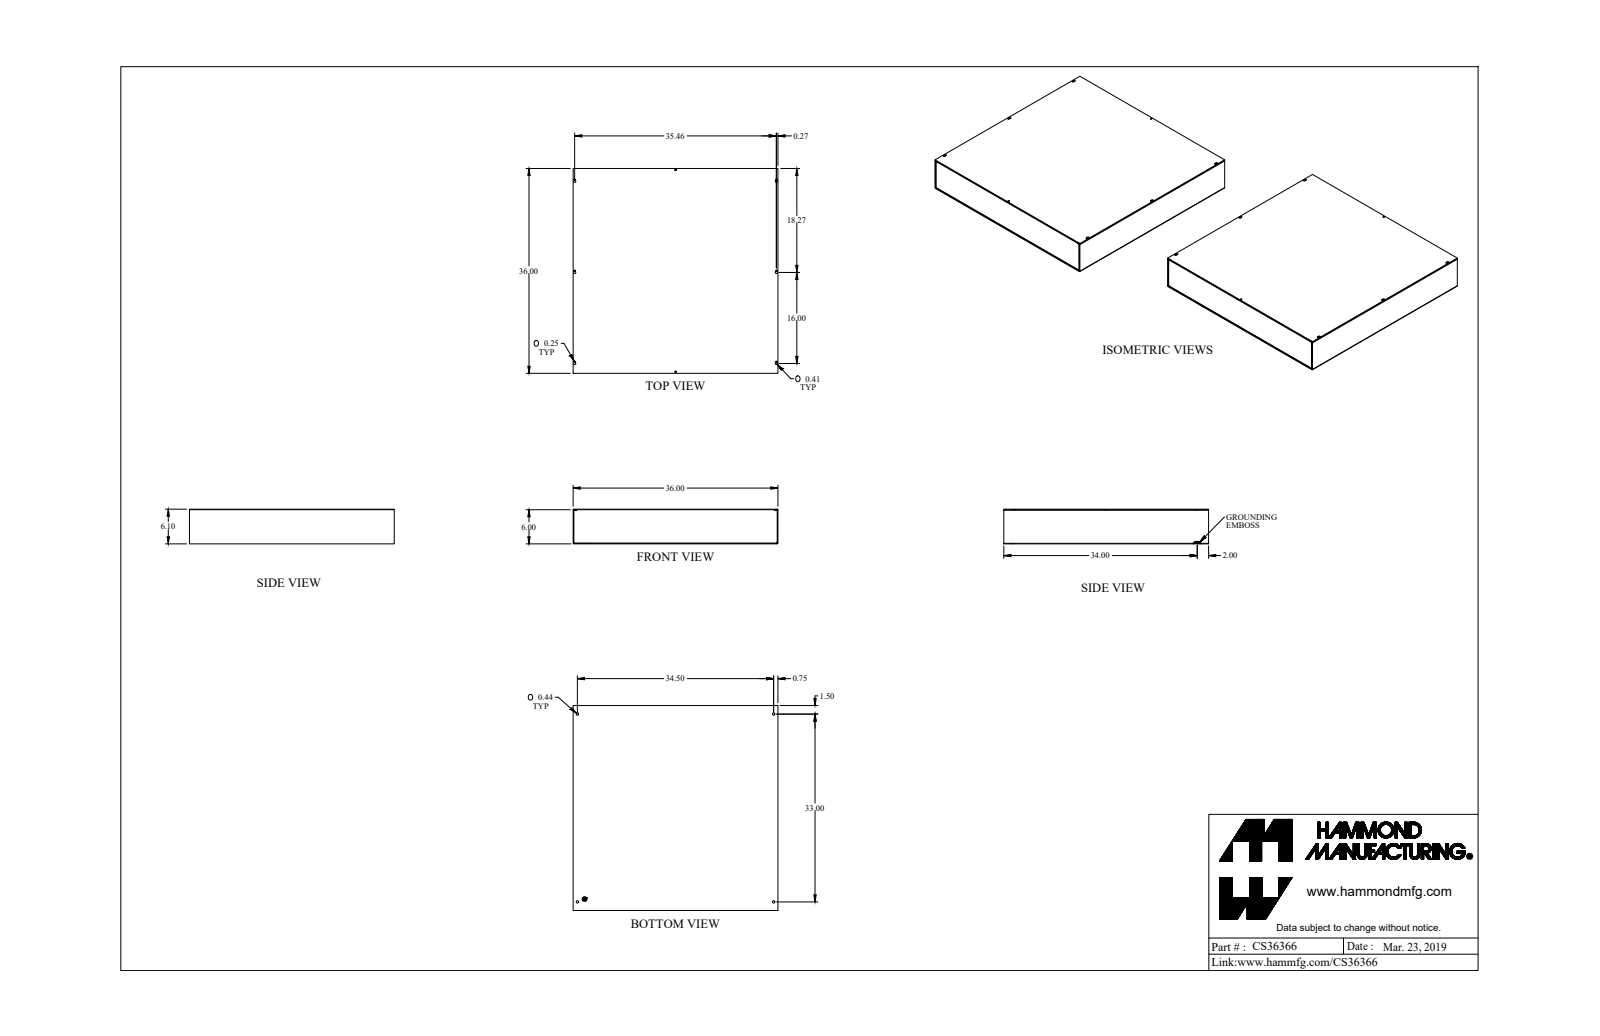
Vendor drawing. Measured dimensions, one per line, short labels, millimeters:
name: CS36366_Default
written by: SolidWorks 2019 (CONFIG_CONTROL_DESIGN)
unit: mm
bodies: 4 solids, 221 faces (121 planar, 92 cylindrical, 8 other)
size: 914.4 × 914.4 × 154.8
volume: 5 496 000 mm³; area: 4 587 000 mm²
holes: 9× ⌀4.3, 4× ⌀11.1, 2× ⌀6.4, 1× ⌀12.7
bosses: 1× ⌀12.5, 1× ⌀9.1
rounds: 12× R1.2, 12× R3.6, 8× R2.4, 6× R3.2, 6× R5.2
face distances: 2.4, 152.4, 150, 154.8, 912, 914.4, 909.6, 2.9, 147.1, 149.5
hole spacings: 17.6, 406.4, 419.3, 439.3, 452.5, 636.9, 825.6, 888.6
